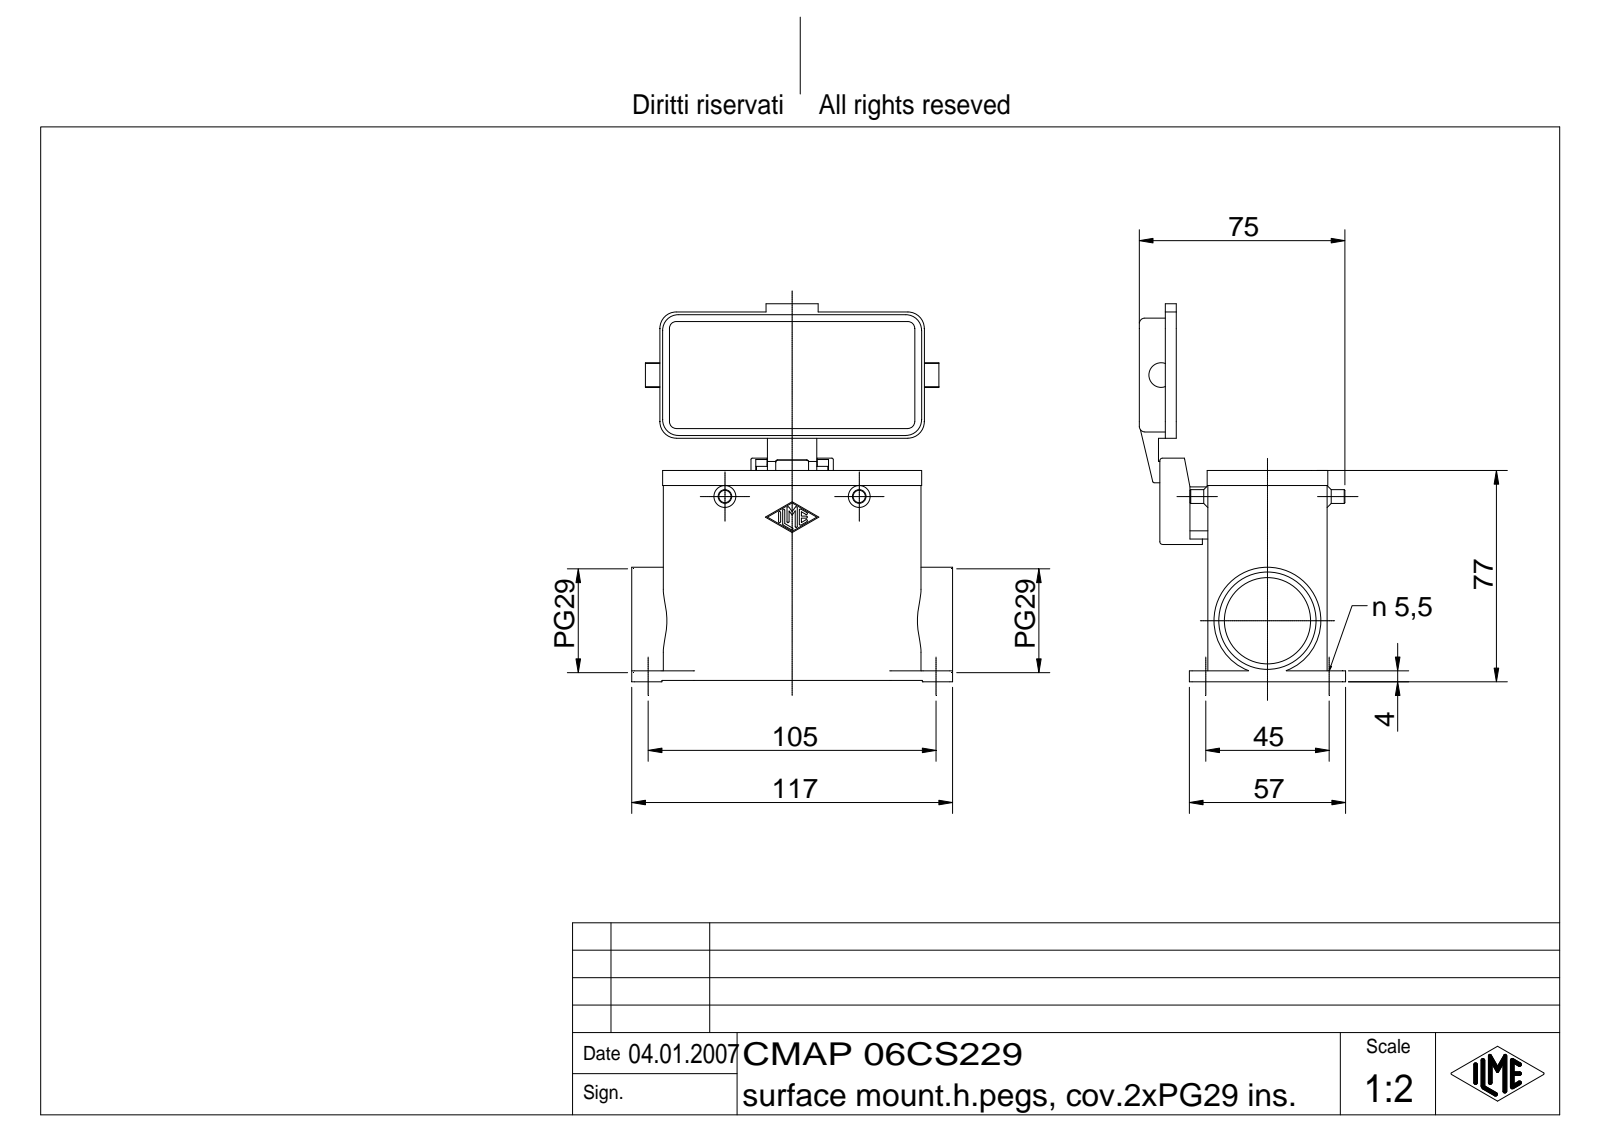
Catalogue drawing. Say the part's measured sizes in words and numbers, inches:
The part is named "CMAP 06CS229". Its 3-D file was written by "Autodesk Inventor 7 (AUTOMOTIVE_DESIGN)". It is 1 solid with 473 faces: 197 planar, 166 cylindrical and 110 other. Overall it measures 5.423 by 4.606 by 2.963 inches. Its volume is 7.249 cubic inches and its surface area 116.4 square inches. Round holes: 4 of diameter 0.217, 1 of diameter 0.157, 1 of diameter 0.197, 1 of diameter 1.239, 1 of diameter 1.397. Round bosses or shafts: 2 of diameter 0.197, 2 of diameter 0.118, 1 of diameter 1.535, 1 of diameter 0.276, 1 of diameter 0.157. Partial cylindrical surfaces (rounded edges, fillets, slot ends): 14 of radius 0.015, 14 of radius 0.039, 12 of radius 0.236, 10 of radius 0.02, 8 of radius 0.028, 8 of radius 0.079, 4 of radius 0.098, 4 of radius 0.118. The main face-to-face distances are 0.118, 1.594, 1.713, 1.476, 0.098, 0.138, 0.886, 2.598, 2.48, 1.004. The hole center spacings are 1.772, 4.134, 4.498.
